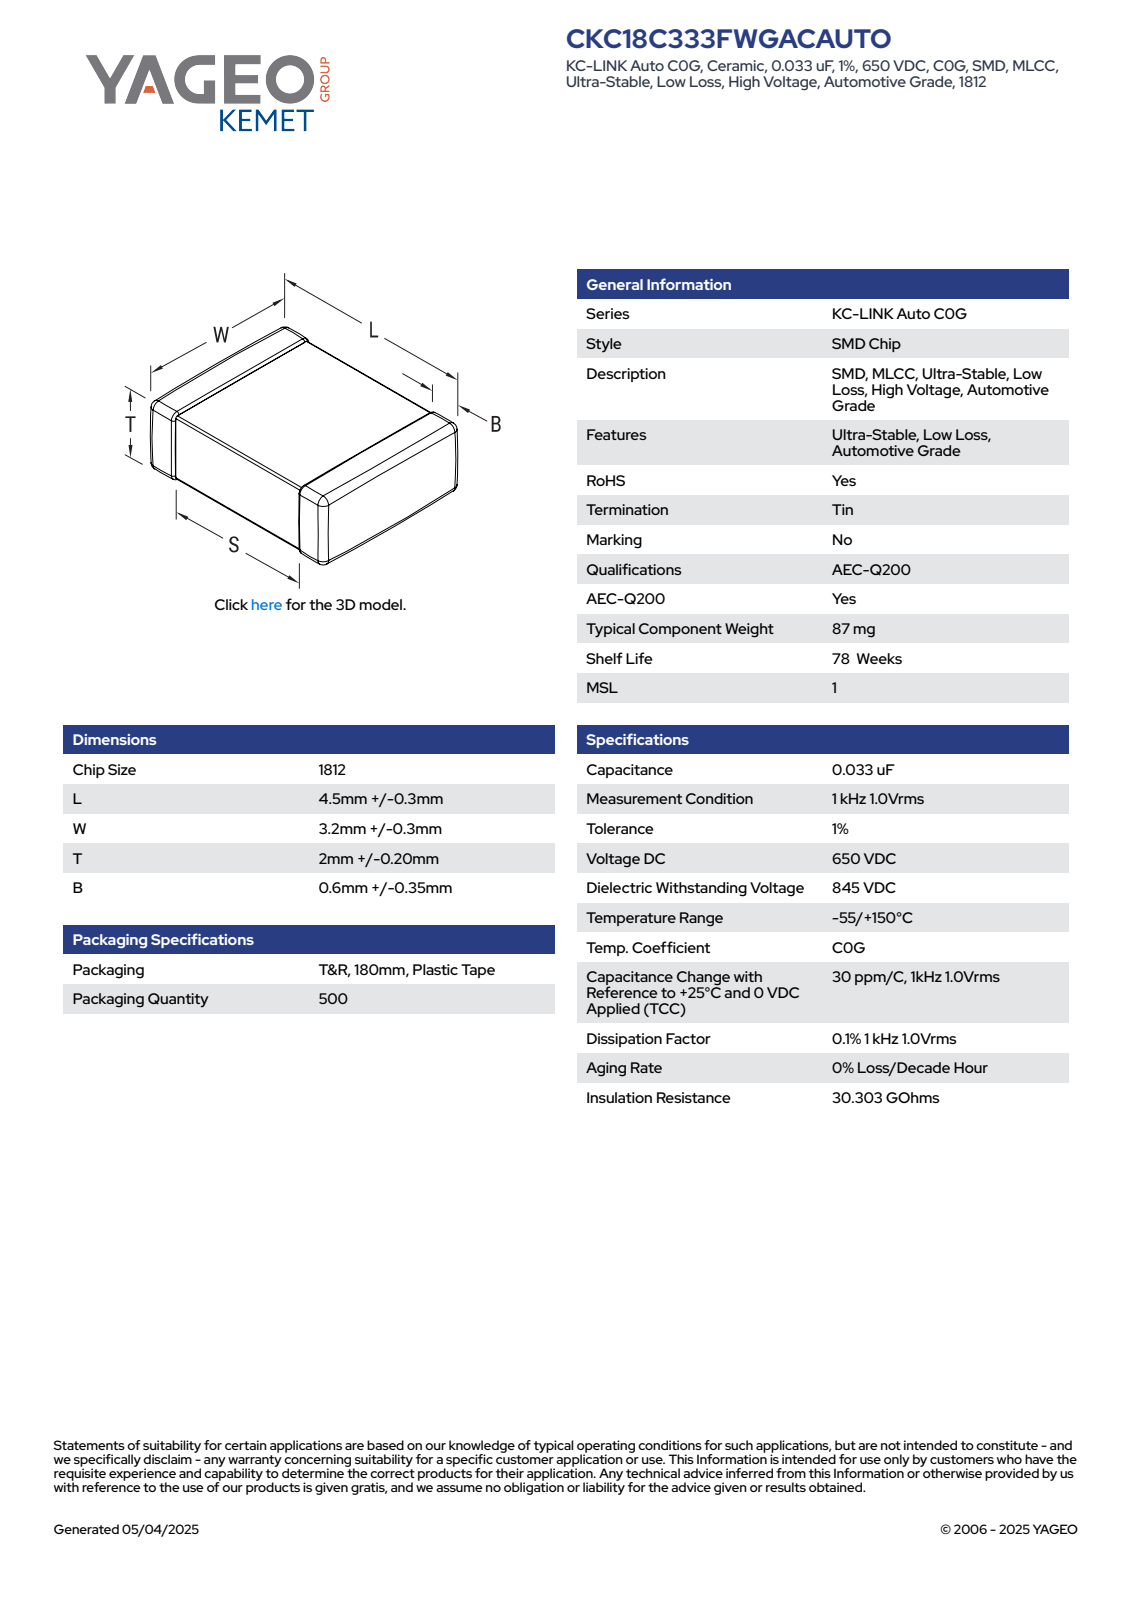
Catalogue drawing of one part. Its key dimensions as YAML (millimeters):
part_name: "CCS_CCSTDNOS_1812_L4.8W3.5T2.2B0.95"
step_written_by: "SolidWorks 2014 (AUTOMOTIVE_DESIGN)"
units: millimeters
bodies: {solids: 4, faces: 121, planar: 71, cylindrical: 34, other: 16}
overall_size: [4.8, 3.5, 2.2]
volume: 35
surface_area: 69
face_to_face_distances: [2.13, 2.06, 4.8, 3.43, 3.36, 2.2, 3.5, 1.49, 0.34, 1.94]
